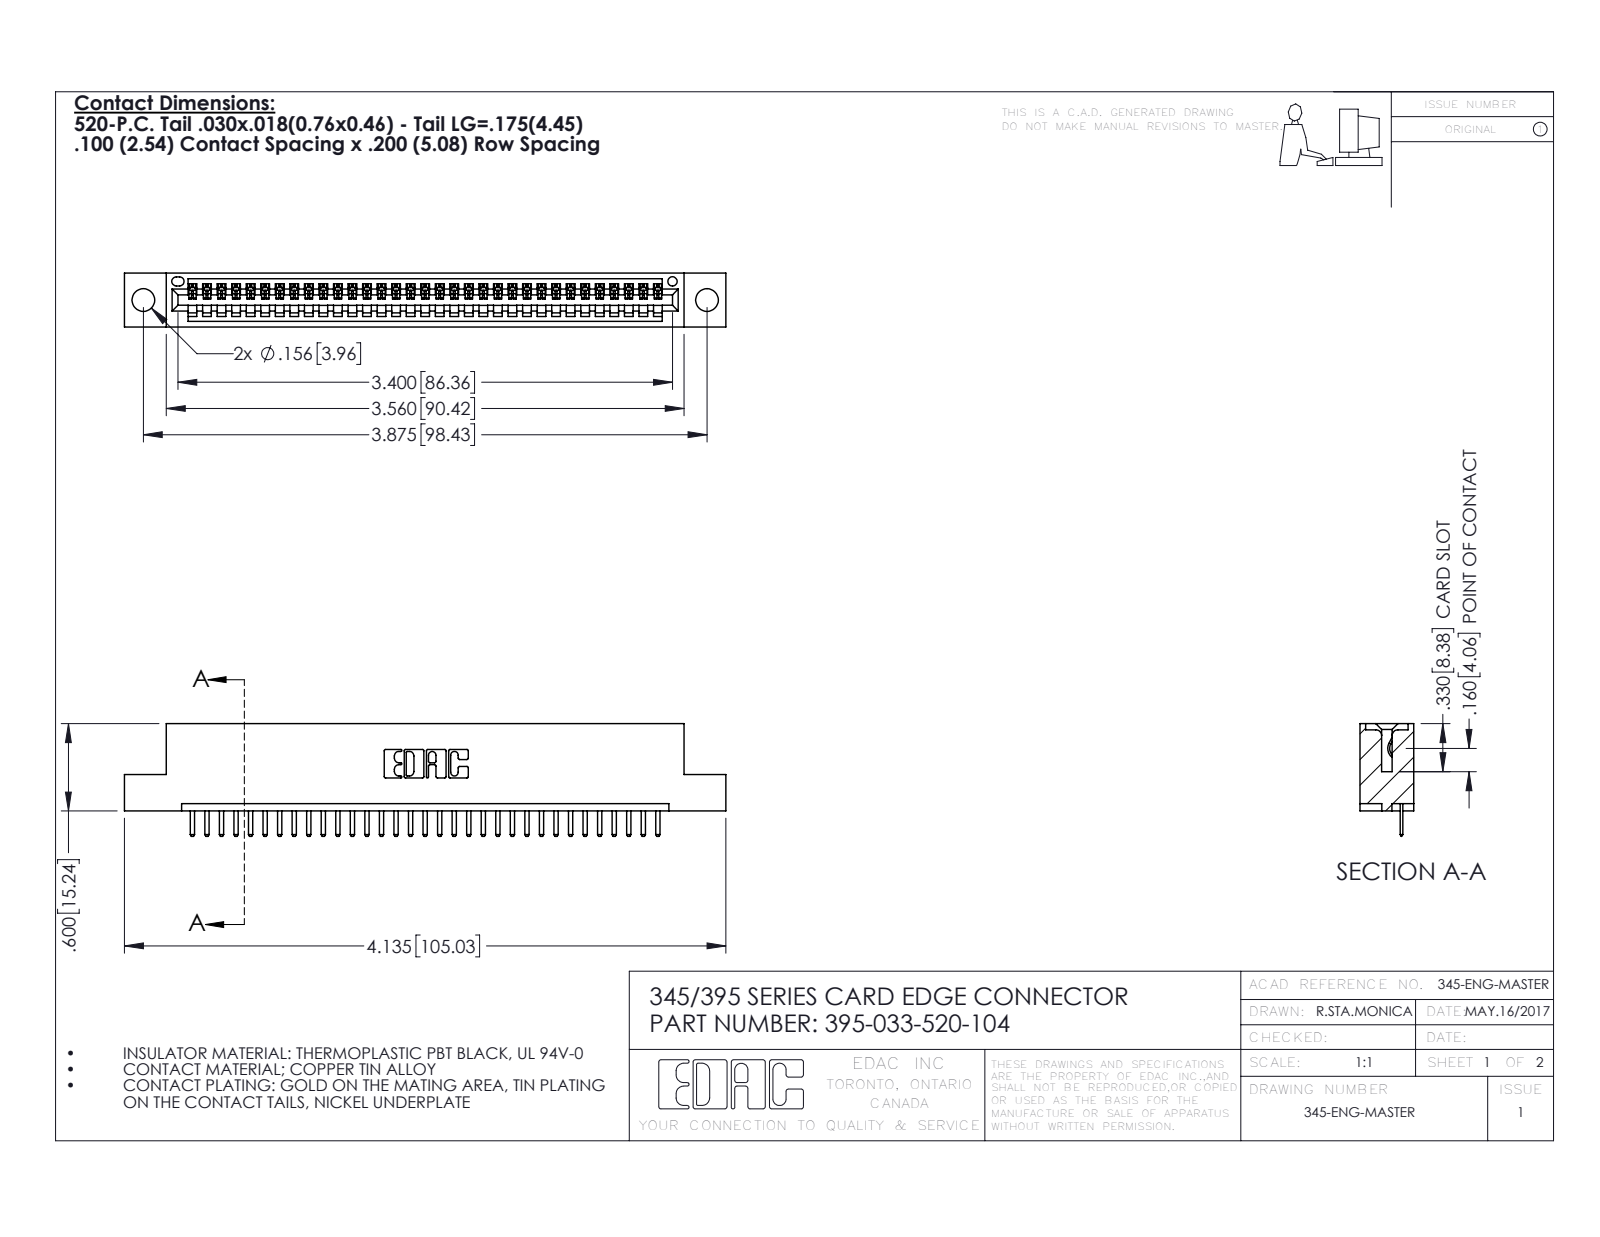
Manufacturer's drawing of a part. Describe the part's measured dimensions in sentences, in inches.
The part is named "395-033-520-104; 345 Part_Flush Mounting Lugs - 0.156 Dia-TH; 345-292-001_345-293-120". Its 3-D file was written by "SolidWorks 2016 (CONFIG_CONTROL_DESIGN)". It is 34 solids with 2172 faces: 1466 planar, 706 cylindrical and 0 other. Overall it measures 4.135 by 0.775 by 0.37 inches. Its volume is 0.593 cubic inches and its surface area 19.05 square inches. Round holes: 2 of diameter 0.156, 1 of diameter 0.064. Partial cylindrical surfaces (rounded edges, fillets, slot ends): 68 of radius 0.01, 66 of radius 0.006, 22 of radius 0.01, 6 of radius 0.007, 6 of radius 0.031, 3 of radius 0.026, 2 of radius 0.031, 2 of radius 0.04. The main face-to-face distances are 0.298, 0.072, 0.37, 0.2, 0.098, 0.272, 0.025, 0.225, 0.072, 0.149. The hole center spacings are 0.27, 3.64, 3.875.
